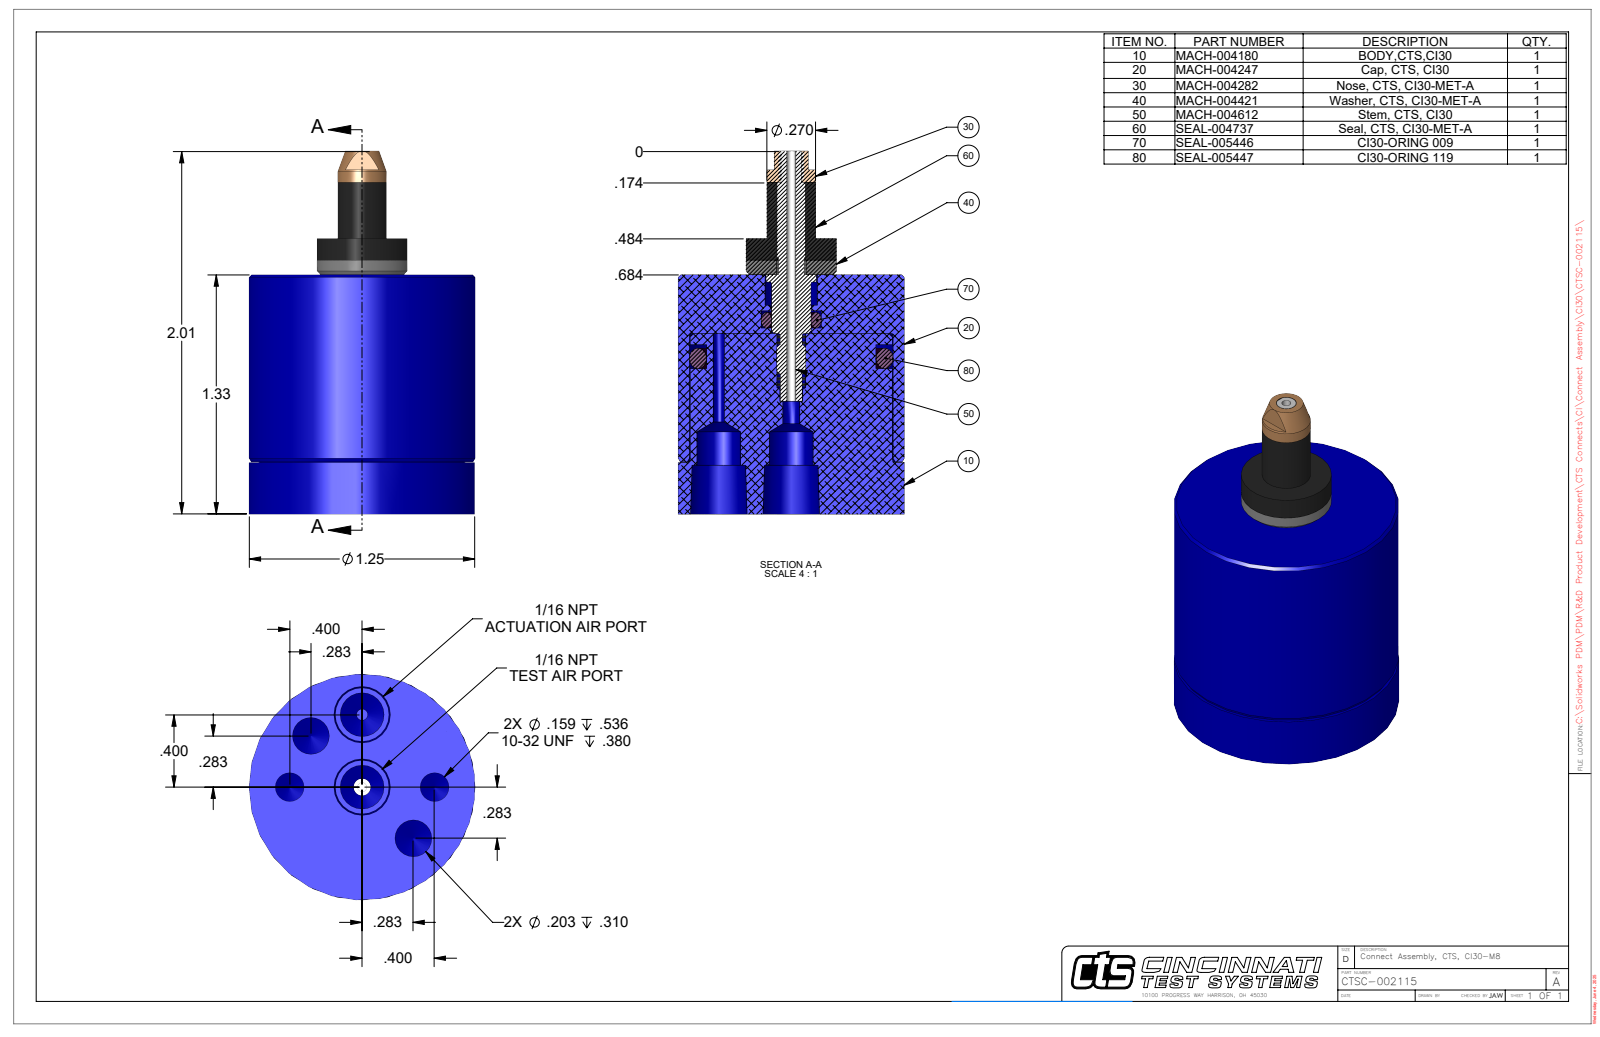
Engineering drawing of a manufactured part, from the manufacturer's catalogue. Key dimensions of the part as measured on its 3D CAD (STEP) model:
Part name (STEP PRODUCT): CTSC-002115
STEP written by: SolidWorks 2023 (AUTOMOTIVE_DESIGN)
Units: inches
Bodies: 1 solid, 89 faces (22 planar, 36 cylindrical, 31 other)
Overall size (bounding box): 2.009 × 1.25 × 1.25
Volume: 1.577 in³ · Surface area: 13.18 in²
Round holes (diameter × count): ⌀0.159 ×2, ⌀0.203 ×2, ⌀0.242 ×2, ⌀0.052 ×1, ⌀0.062 ×1, ⌀0.094 ×1, ⌀0.113 ×1, ⌀0.289 ×1, ⌀1.125 ×1
Round bosses / shafts (diameter × count): ⌀1.25 ×1, ⌀1.115 ×1, ⌀0.5 ×1, ⌀0.277 ×1, ⌀0.27 ×1
Main face-to-face distances: 1.325, 0.287, 1.039, 0.29, 1.035, 1.525, 1.239, 1.235, 0.2, 0.271
Hole centre spacings: 0.306, 0.4, 0.739, 0.4, 0.566, 0.8, 0.8
